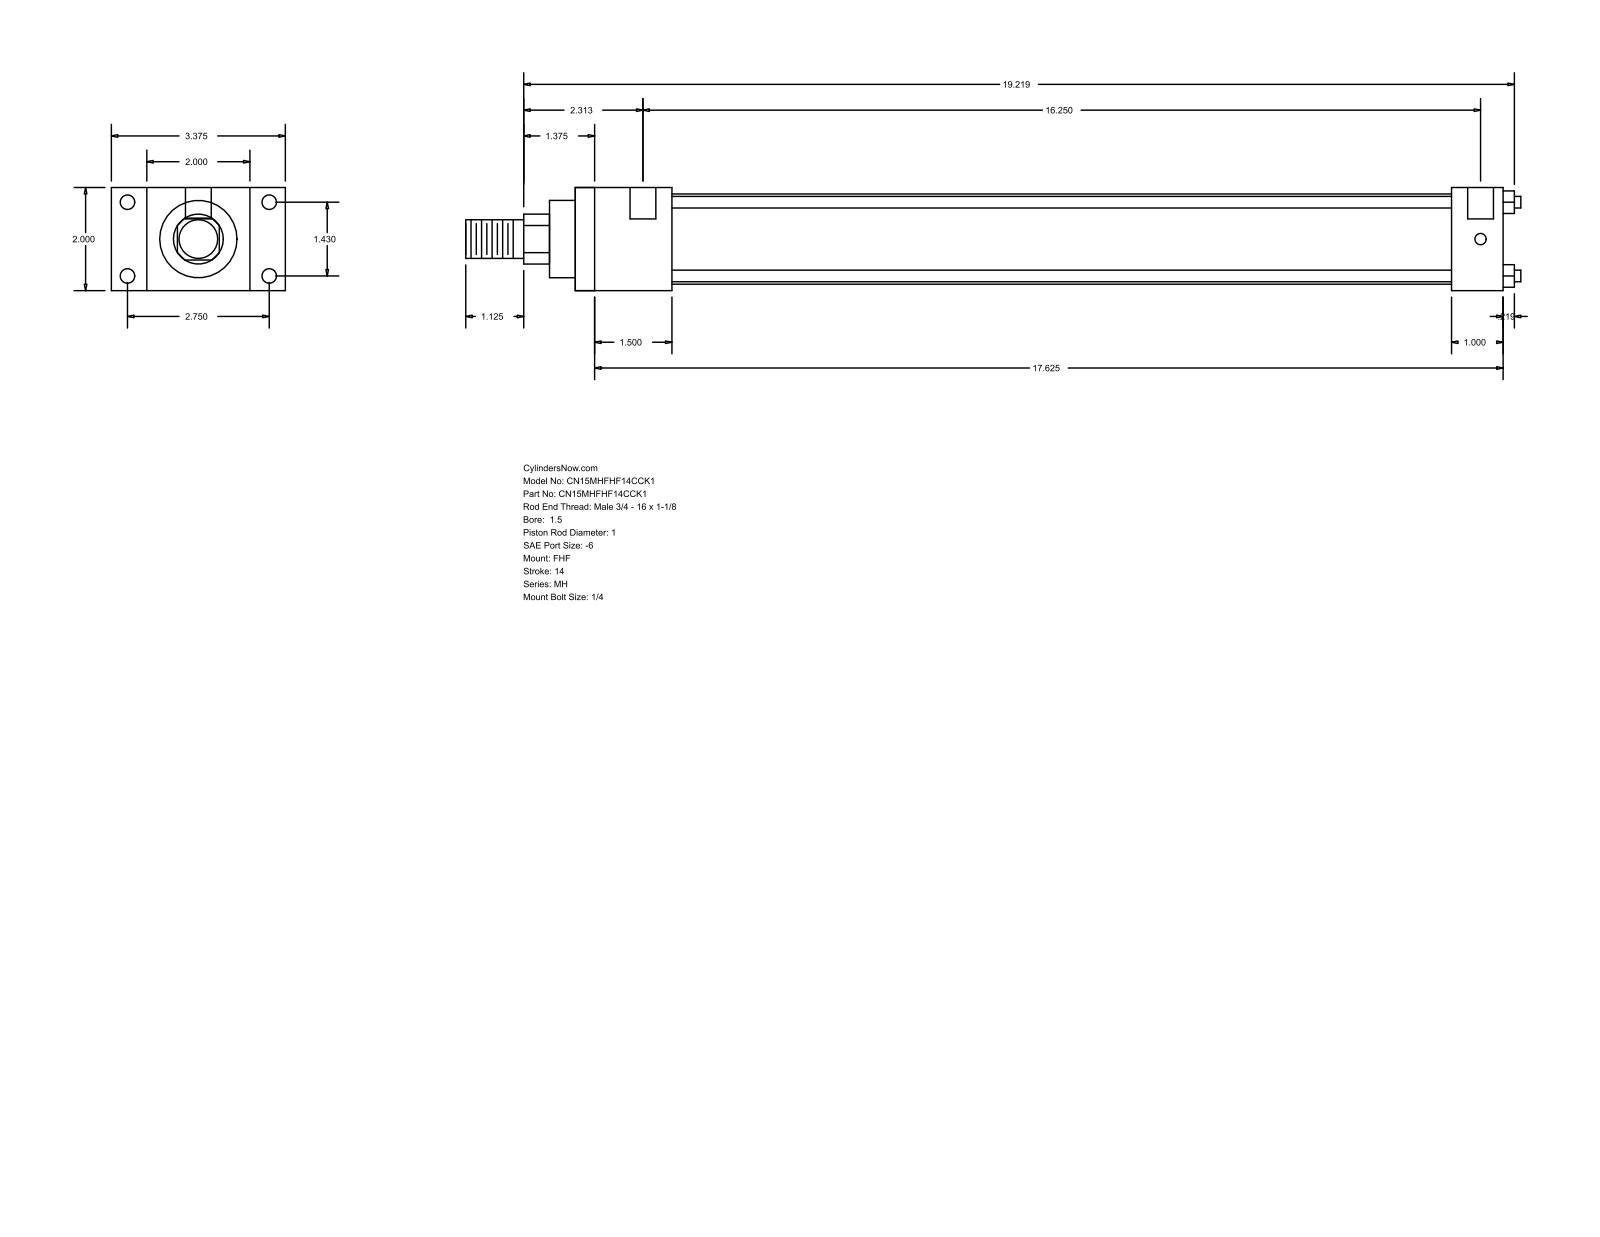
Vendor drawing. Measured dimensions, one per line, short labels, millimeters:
name: MH_FHF__0150_1
written by: GSSL Pune (CONFIG_CONTROL_DESIGN)
unit: mm
bodies: 0 solids, 88 faces (60 planar, 28 cylindrical, 0 other)
size: 519.91 × 85.72 × 50.8
holes: 4× ⌀5.56, 4× ⌀7.14, 2× ⌀12.7
bosses: 4× ⌀5.71, 1× ⌀44.45, 1× ⌀38.1, 1× ⌀25.4, 1× ⌀19.05
rounds: 1× R12.29
face distances: 50.8, 17.46, 68.26, 47.63, 85.72, 457.2, 409.57, 25.4, 431.8, 384.17
hole spacings: 36.32, 69.84, 78.72, 415.93, 3.18, 412.75
